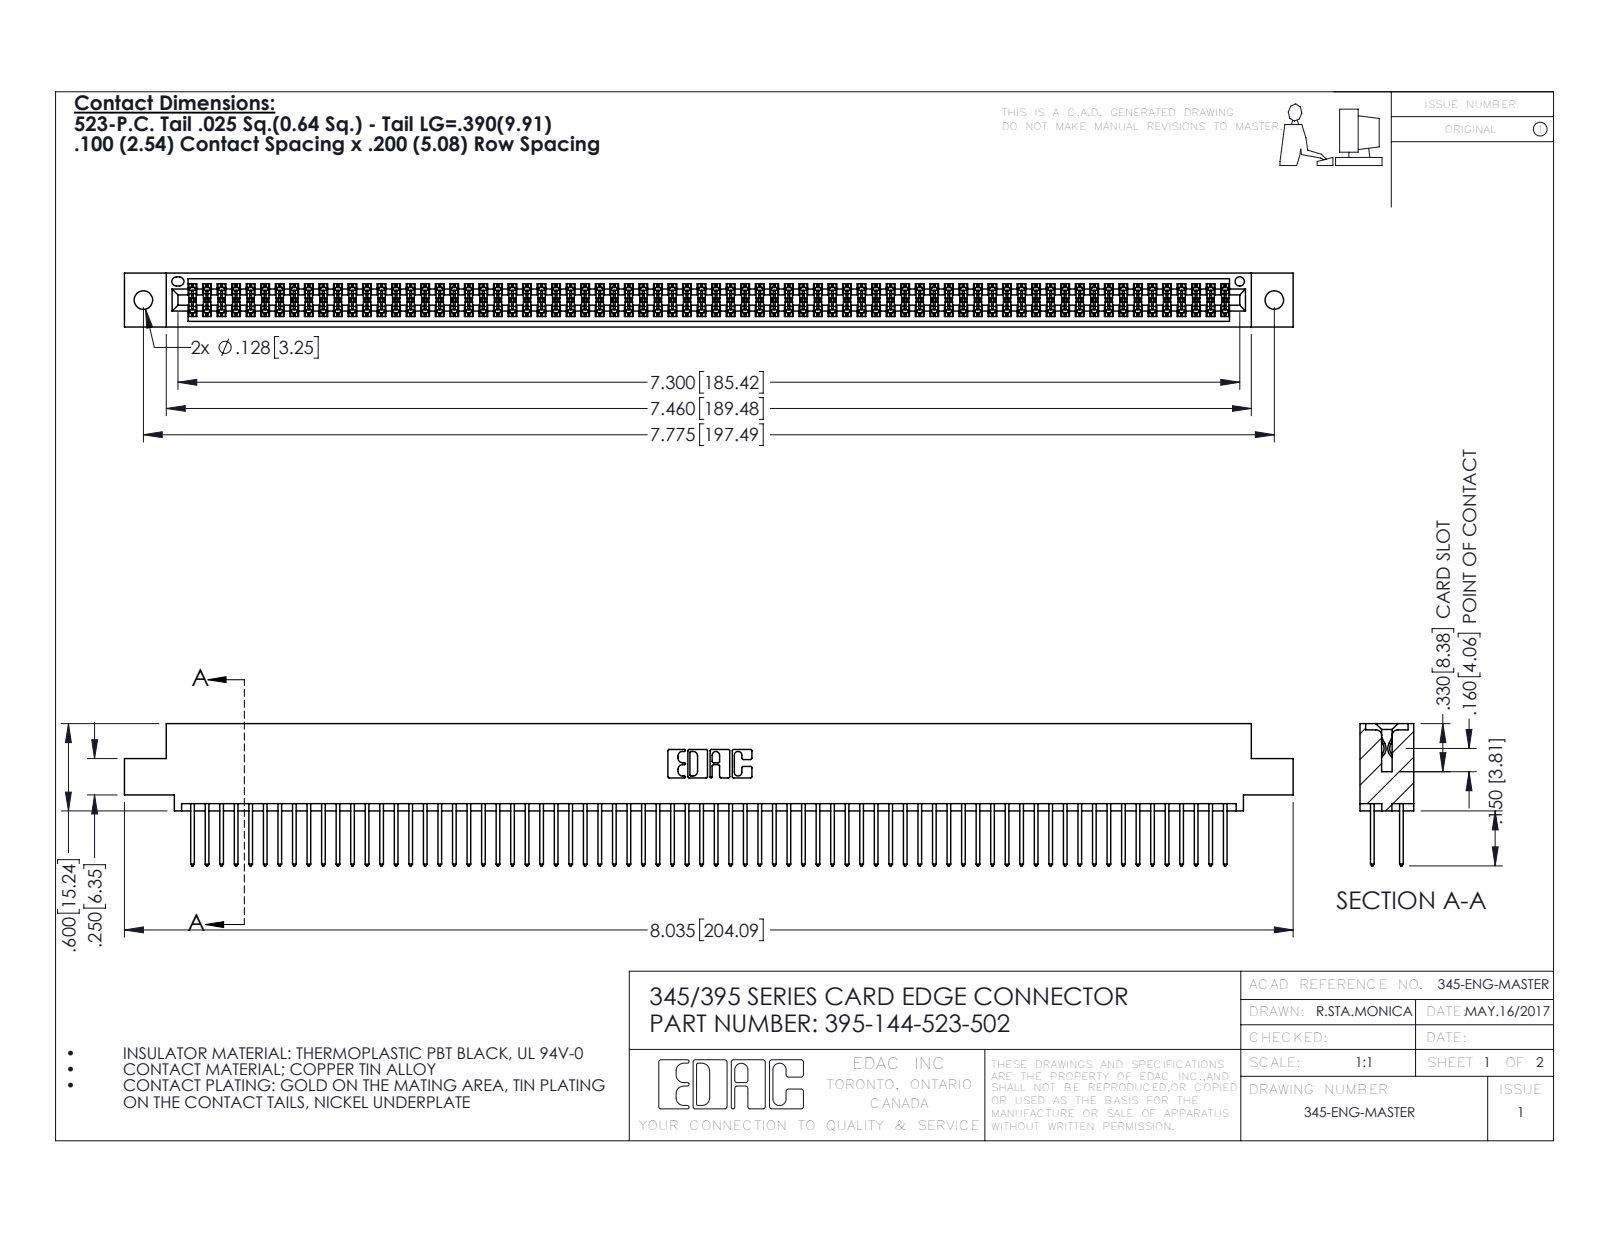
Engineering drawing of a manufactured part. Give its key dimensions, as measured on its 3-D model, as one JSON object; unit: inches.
{"part_name": "345-292-001_345-293-123; 345 Part_0.110 Offset - 0.128 Dia; 395-144-523-502", "step_written_by": "SolidWorks 2016 (CONFIG_CONTROL_DESIGN)", "units": "inches", "bodies": {"solids": 145, "faces": 7330, "planar": 4836, "cylindrical": 2494, "other": 0}, "overall_size": [8.035, 0.977, 0.37], "volume_in3": 1.238, "surface_area_in2": 49.16, "round_holes": [[0.128, 2], [0.064, 1]], "partial_cylinders_radius": [[0.006, 216], [0.01, 144], [0.01, 22], [0.007, 6], [0.031, 6], [0.026, 3], [0.014, 2], [0.019, 2]], "face_to_face_distances": [0.072, 0.298, 0.2, 0.098, 0.272, 0.025, 0.37, 0.225, 0.175, 0.149], "hole_center_spacings": [0.27, 7.539, 7.775]}
